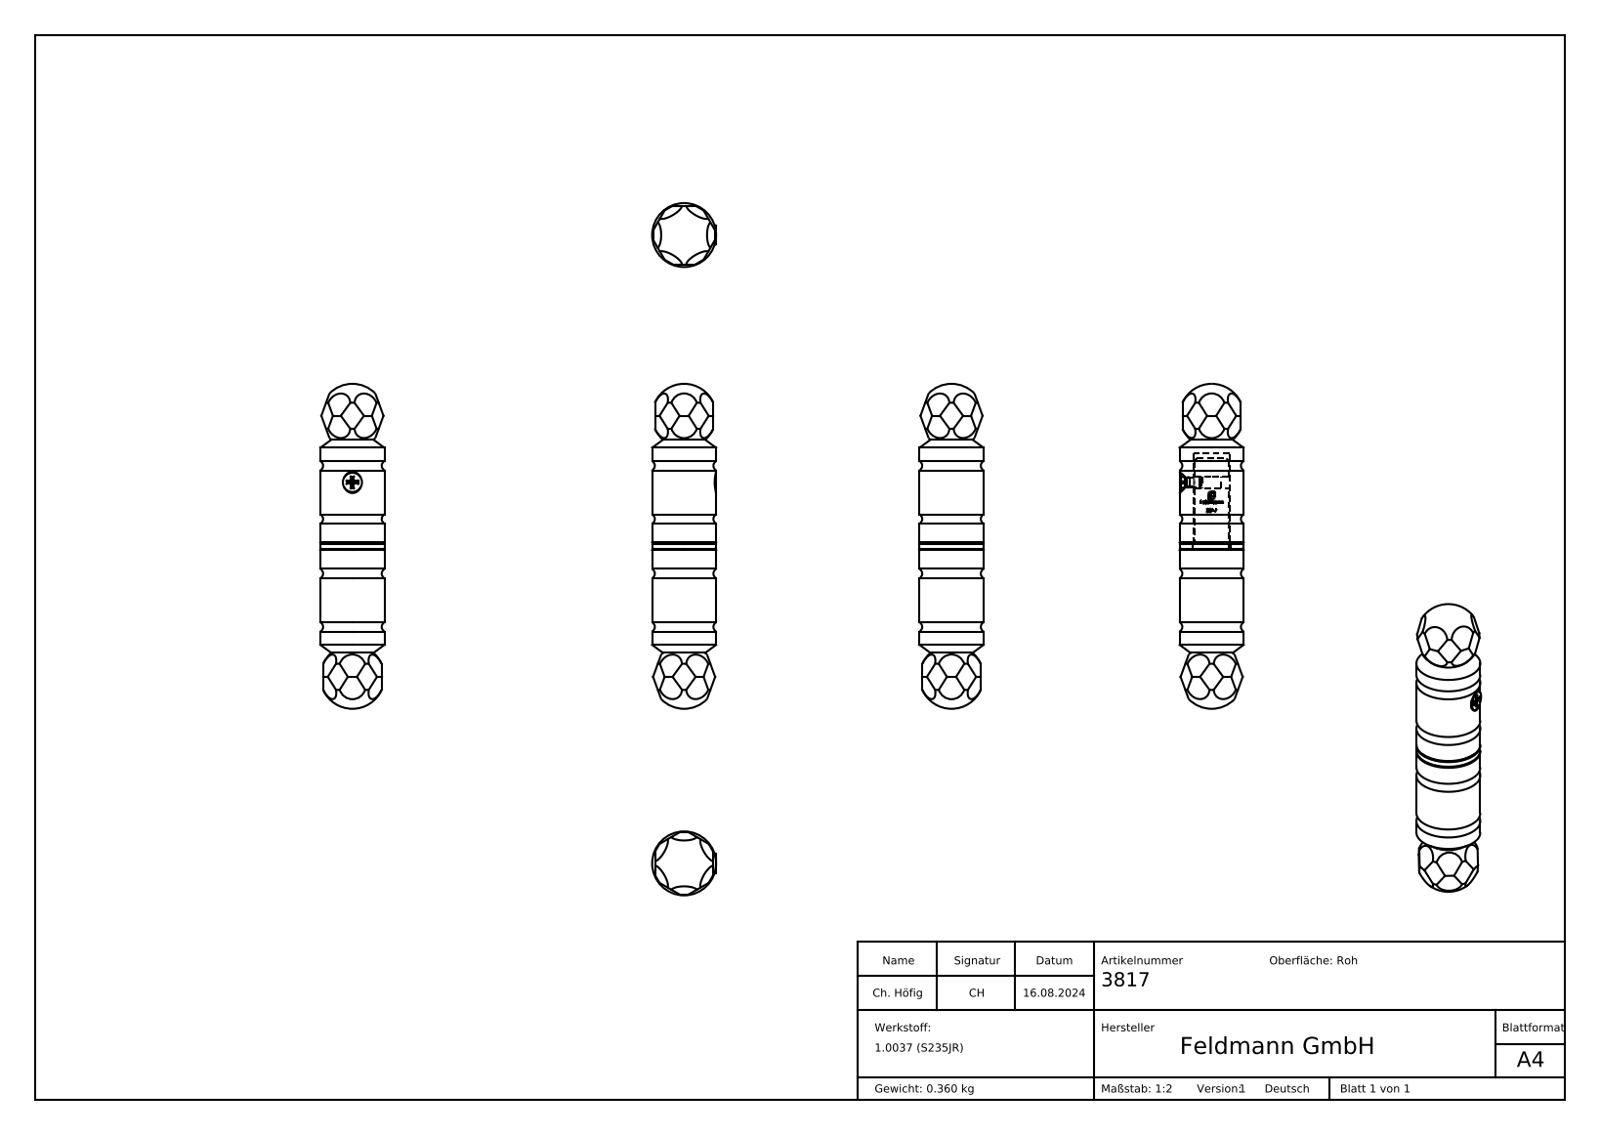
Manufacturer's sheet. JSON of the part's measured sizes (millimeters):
{"part_name": "3817; 3817 und 3818 Teil1-3_3817 Teil3; DIN 965_DIN 965 M4x8; 3817 und 3818 Teil1-3_3817 Teil2 (+1 more)", "step_written_by": "SolidWorks 2018 (CONFIG_CONTROL_DESIGN)", "units": "millimeters", "bodies": {"solids": 4, "faces": 301, "planar": 150, "cylindrical": 34, "other": 117}, "overall_size": [122, 24, 24], "volume_mm3": 46124, "surface_area_mm2": 14062, "round_holes": [[3.3, 1], [13.5, 1], [14, 1]], "round_bosses_or_shafts": [[24, 1], [13, 1], [7.2, 1], [7, 1], [4, 1], [3.6, 1]], "partial_cylinders_radius": [[6.85, 1]], "face_to_face_distances": [21.9, 2, 21.91, 34, 36, 32, 11.1, 13.1, 22.9, 20.9]}
